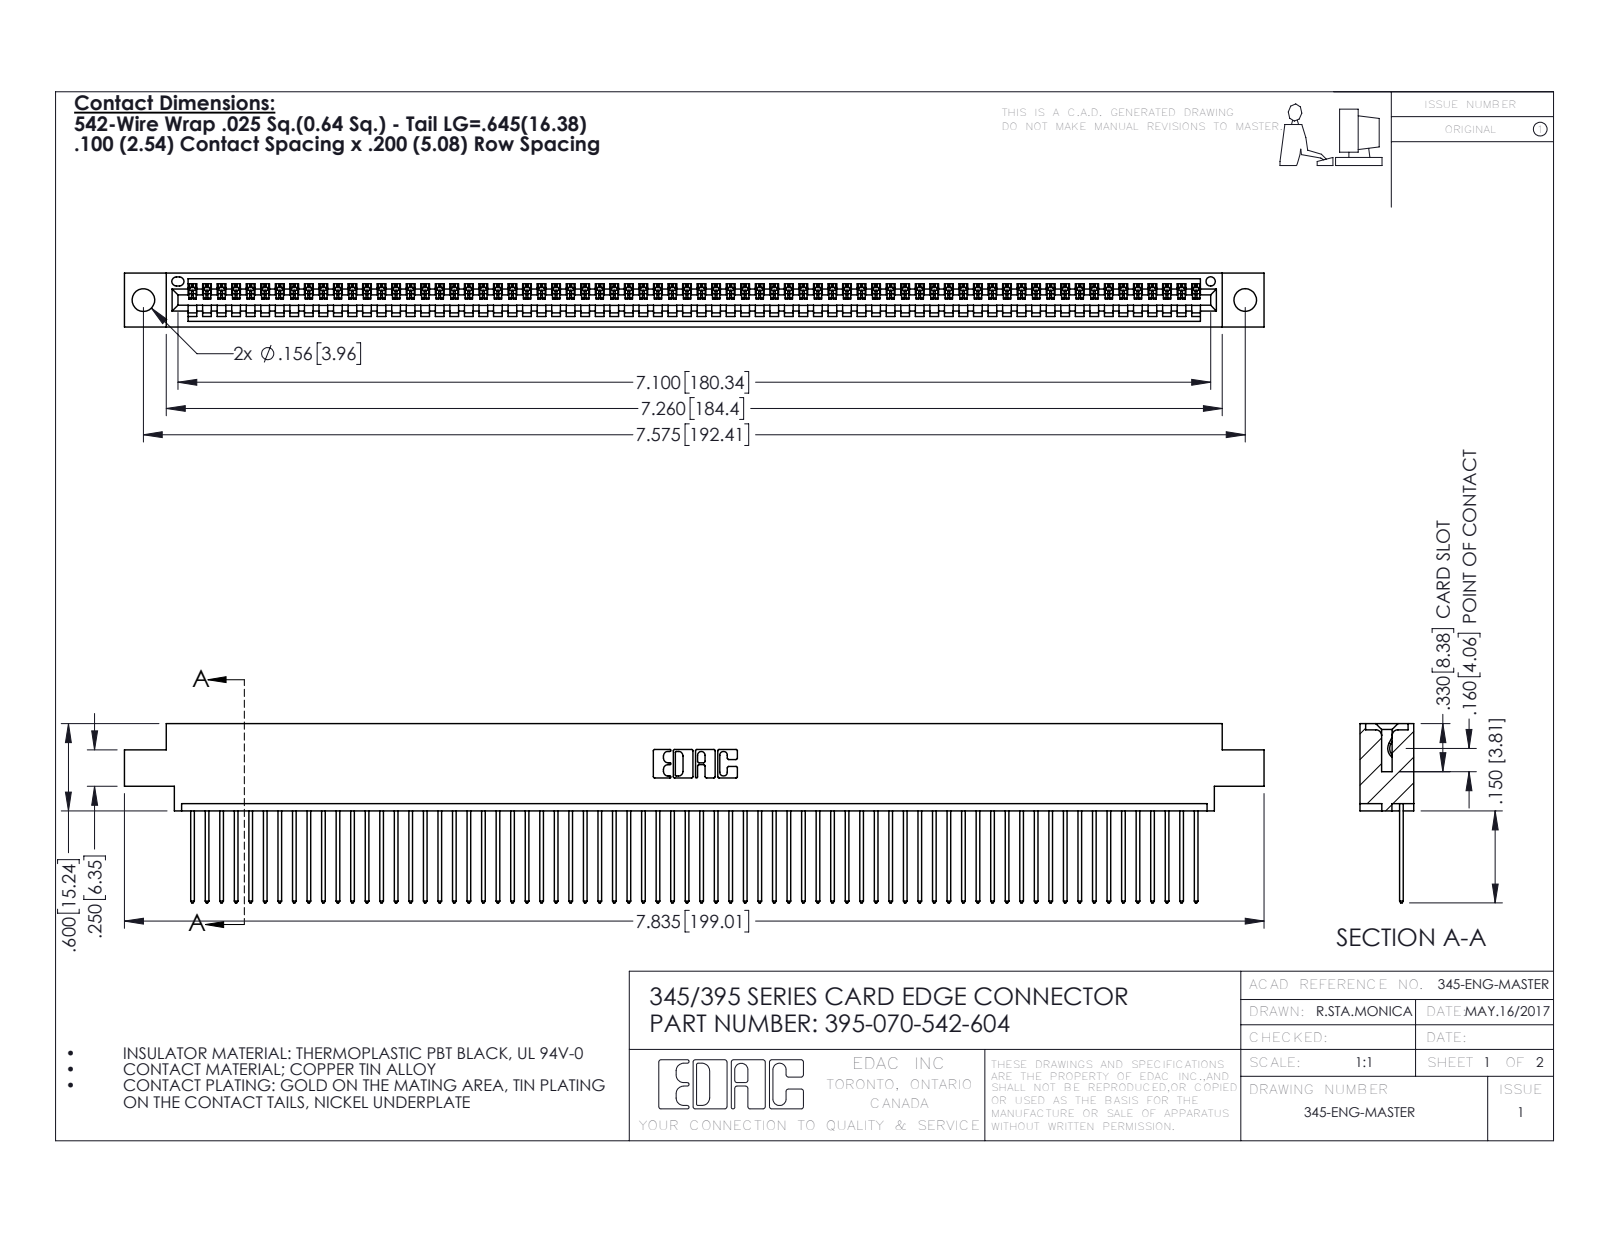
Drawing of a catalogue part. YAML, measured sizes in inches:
part_name: "345-292-001_345-293-142; 345 Part_0.170 Offset - 0.156 Dia-TH; 395-070-542-604"
step_written_by: "SolidWorks 2016 (CONFIG_CONTROL_DESIGN)"
units: inches
bodies: {solids: 71, faces: 4190, planar: 2884, cylindrical: 1306, other: 0}
overall_size: [7.835, 1.232, 0.37]
volume: 1.165
surface_area: 41.33
round_holes:
  - {diameter: 0.156, count: 2}
  - {diameter: 0.064, count: 1}
partial_cylinders:
  - {radius: 0.006, count: 140}
  - {radius: 0.01, count: 140}
  - {radius: 0.01, count: 22}
  - {radius: 0.007, count: 6}
  - {radius: 0.031, count: 6}
  - {radius: 0.026, count: 3}
  - {radius: 0.031, count: 2}
  - {radius: 0.04, count: 2}
face_to_face_distances: [0.072, 0.298, 0.37, 0.098, 0.272, 0.025, 0.2, 0.225, 0.175, 0.149]
hole_center_spacings: [0.27, 7.339, 7.575]
